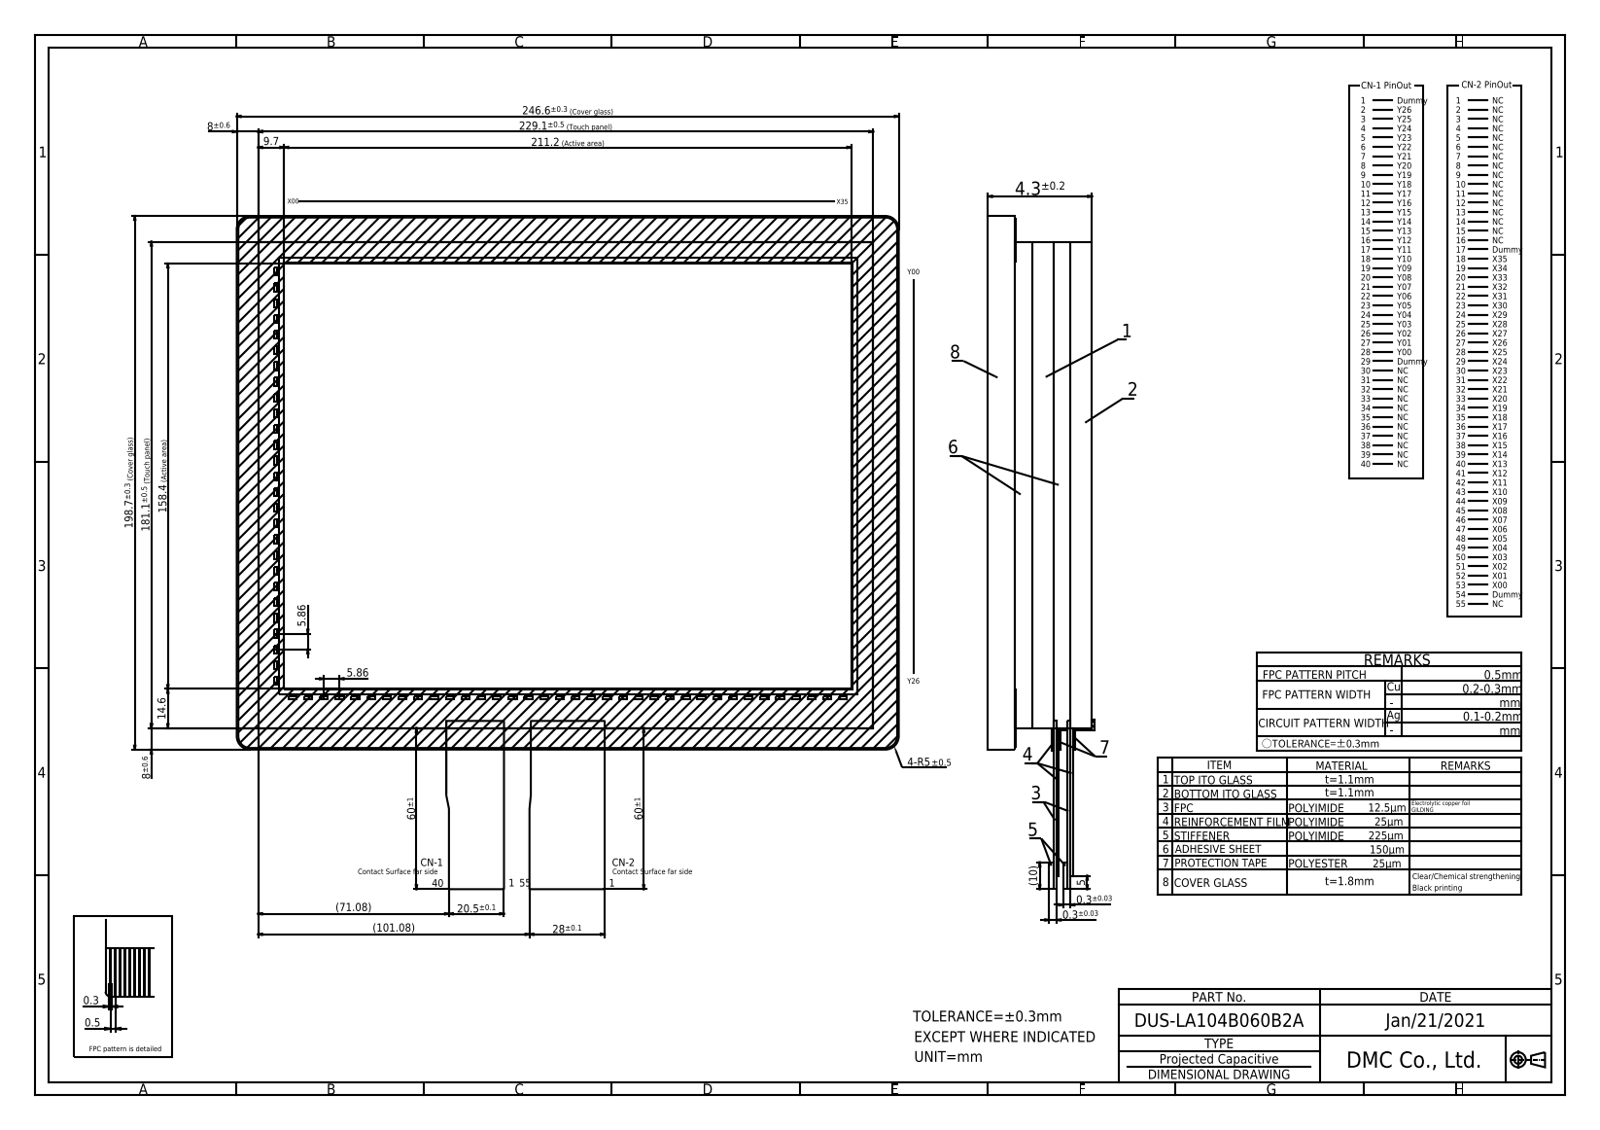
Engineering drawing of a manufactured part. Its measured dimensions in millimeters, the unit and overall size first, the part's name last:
Units: millimetres
Overall size (bounding box): 380.8 × 304.9 × 4.3
Partial cylindrical surfaces — rounded edges, fillets, slot ends (radius × count): R5 ×4, R0.2 ×1
Main face-to-face distances: 1.8, 2.5, 4.3, 2.4, 1.9, 1.25, 1.15, 1.35, 3.15, 3.05
Volume: 206 507 mm³ · Surface area: 194 155 mm²
Bodies: 1 solid, 425 faces (420 planar, 5 cylindrical, 0 other)
Part name (STEP PRODUCT): DUS-LA104B060B2A
STEP written by: Autodesk Inventor 2020 (CONFIG_CONTROL_DESIGN)
